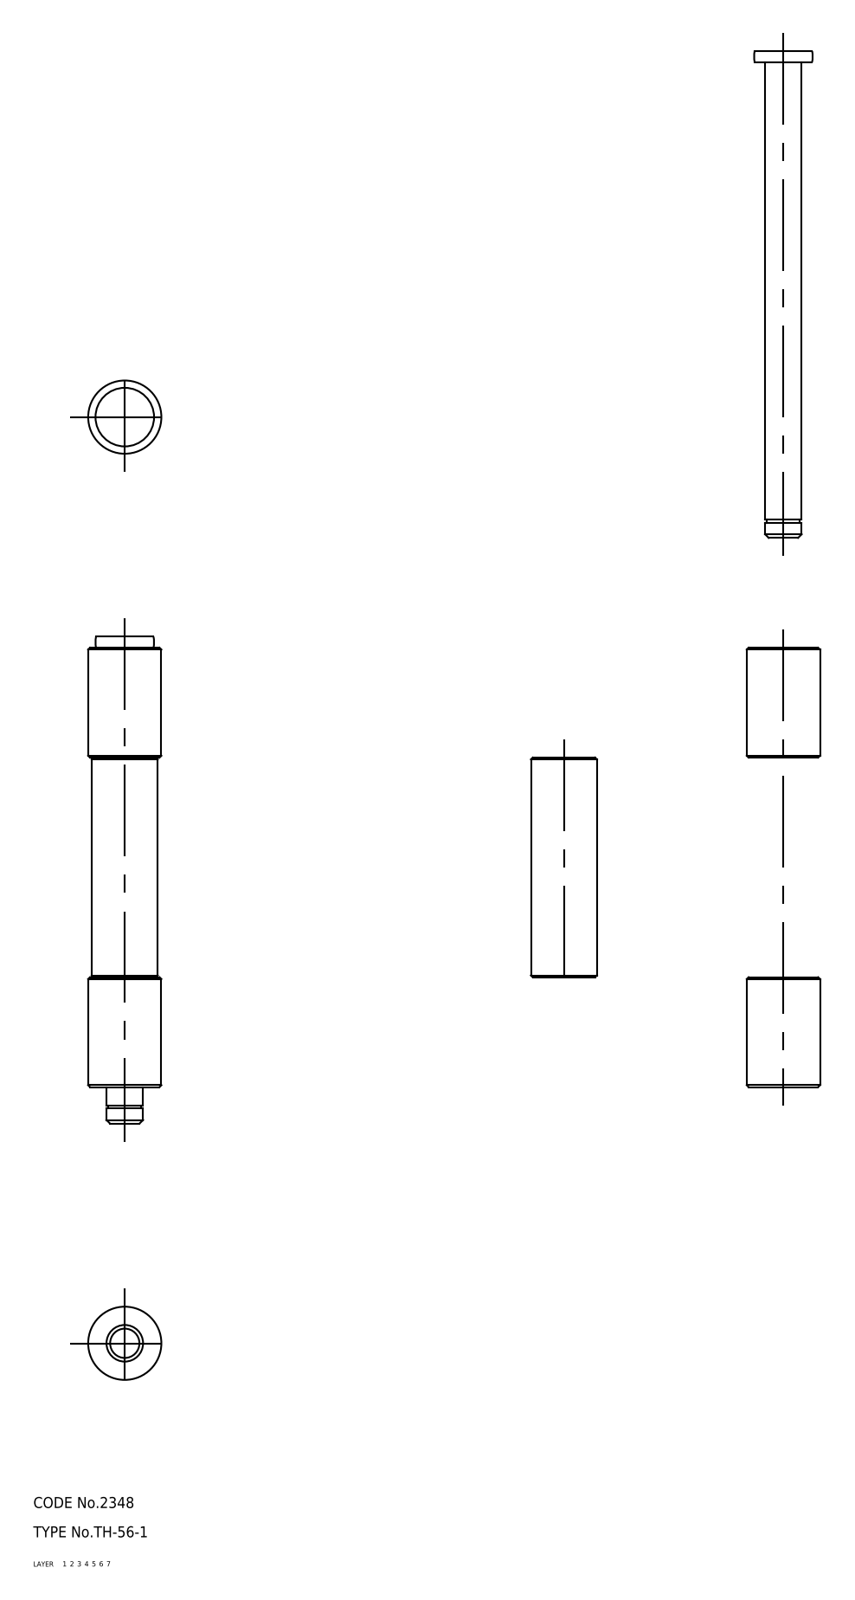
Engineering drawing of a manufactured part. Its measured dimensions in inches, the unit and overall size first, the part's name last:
Units: inches
Overall size (bounding box): 5.236 × 0.787 × 0.787
Volume: 2.166 in³ · Surface area: 25.98 in²
Bodies: 4 solids, 44 faces (0 planar, 0 cylindrical, 44 other)
Part name (STEP PRODUCT): collar_A; shaft; collar_B; TH_56_1_11367_36
STEP written by: CADfix (AUTOMOTIVE_DESIGN)
